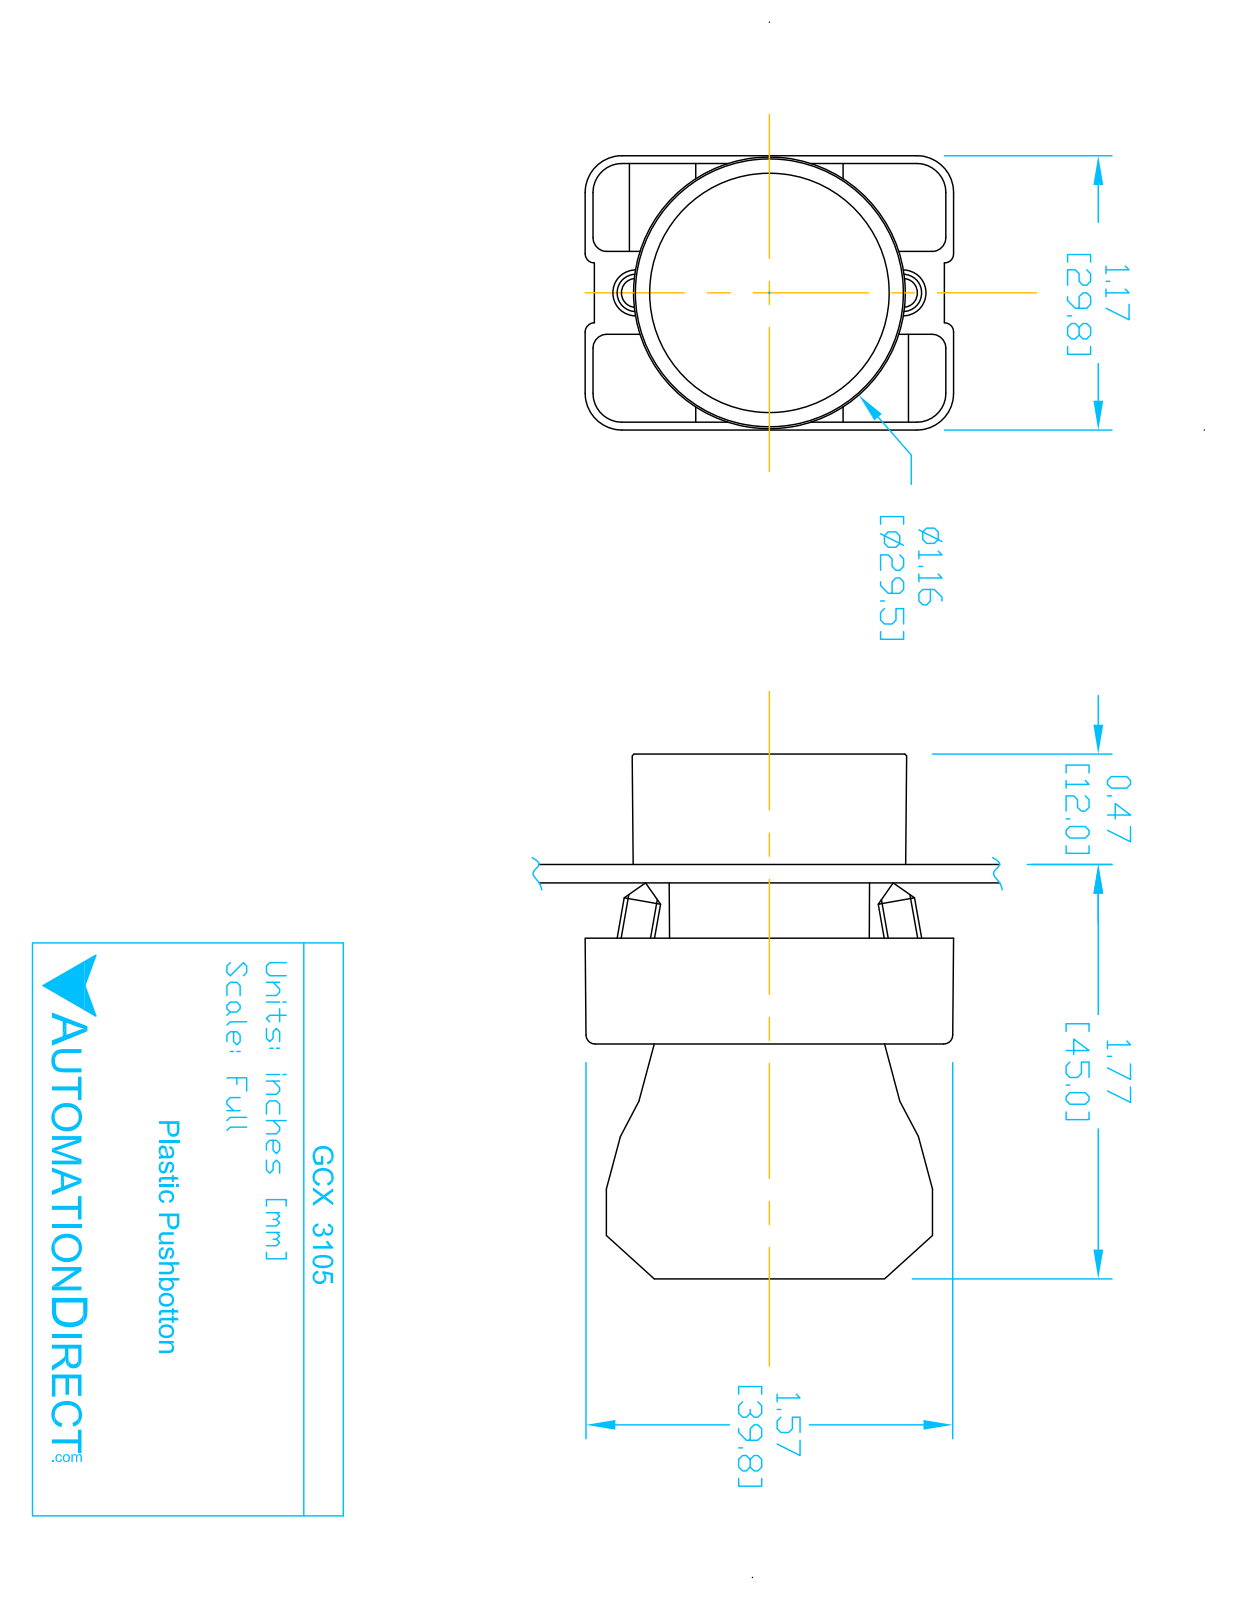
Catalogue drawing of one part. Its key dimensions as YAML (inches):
part_name: "GCX3105; ecx1040; GCX3105 OPERATOR; ECX3029-2"
step_written_by: "SolidWorks 2016 (AUTOMOTIVE_DESIGN)"
units: inches
bodies: {solids: 6, faces: 381, planar: 222, cylindrical: 132, other: 27}
overall_size: [2.217, 1.581, 1.177]
volume: 1.741
surface_area: 27.14
round_holes:
  - {diameter: 0.079, count: 2}
  - {diameter: 0.124, count: 2}
  - {diameter: 0.13, count: 2}
  - {diameter: 0.087, count: 1}
  - {diameter: 0.197, count: 1}
  - {diameter: 0.878, count: 1}
  - {diameter: 0.888, count: 1}
  - {diameter: 1.024, count: 1}
round_bosses_or_shafts:
  - {diameter: 0.157, count: 2}
  - {diameter: 1.175, count: 1}
  - {diameter: 1.004, count: 1}
  - {diameter: 0.945, count: 1}
  - {diameter: 0.856, count: 1}
  - {diameter: 0.78, count: 1}
partial_cylinders:
  - {radius: 0.059, count: 24}
  - {radius: 0.041, count: 12}
  - {radius: 0.124, count: 12}
  - {radius: 0.157, count: 12}
  - {radius: 0.039, count: 4}
  - {radius: 0.128, count: 2}
  - {radius: 0.02, count: 1}
  - {radius: 0.063, count: 1}
face_to_face_distances: [0.72, 0.579, 0.033, 0.472, 1.193, 0.031, 0.689, 0.598, 1.161, 1.071]
hole_center_spacings: [0.236, 0.544, 0.472, 0.49]
